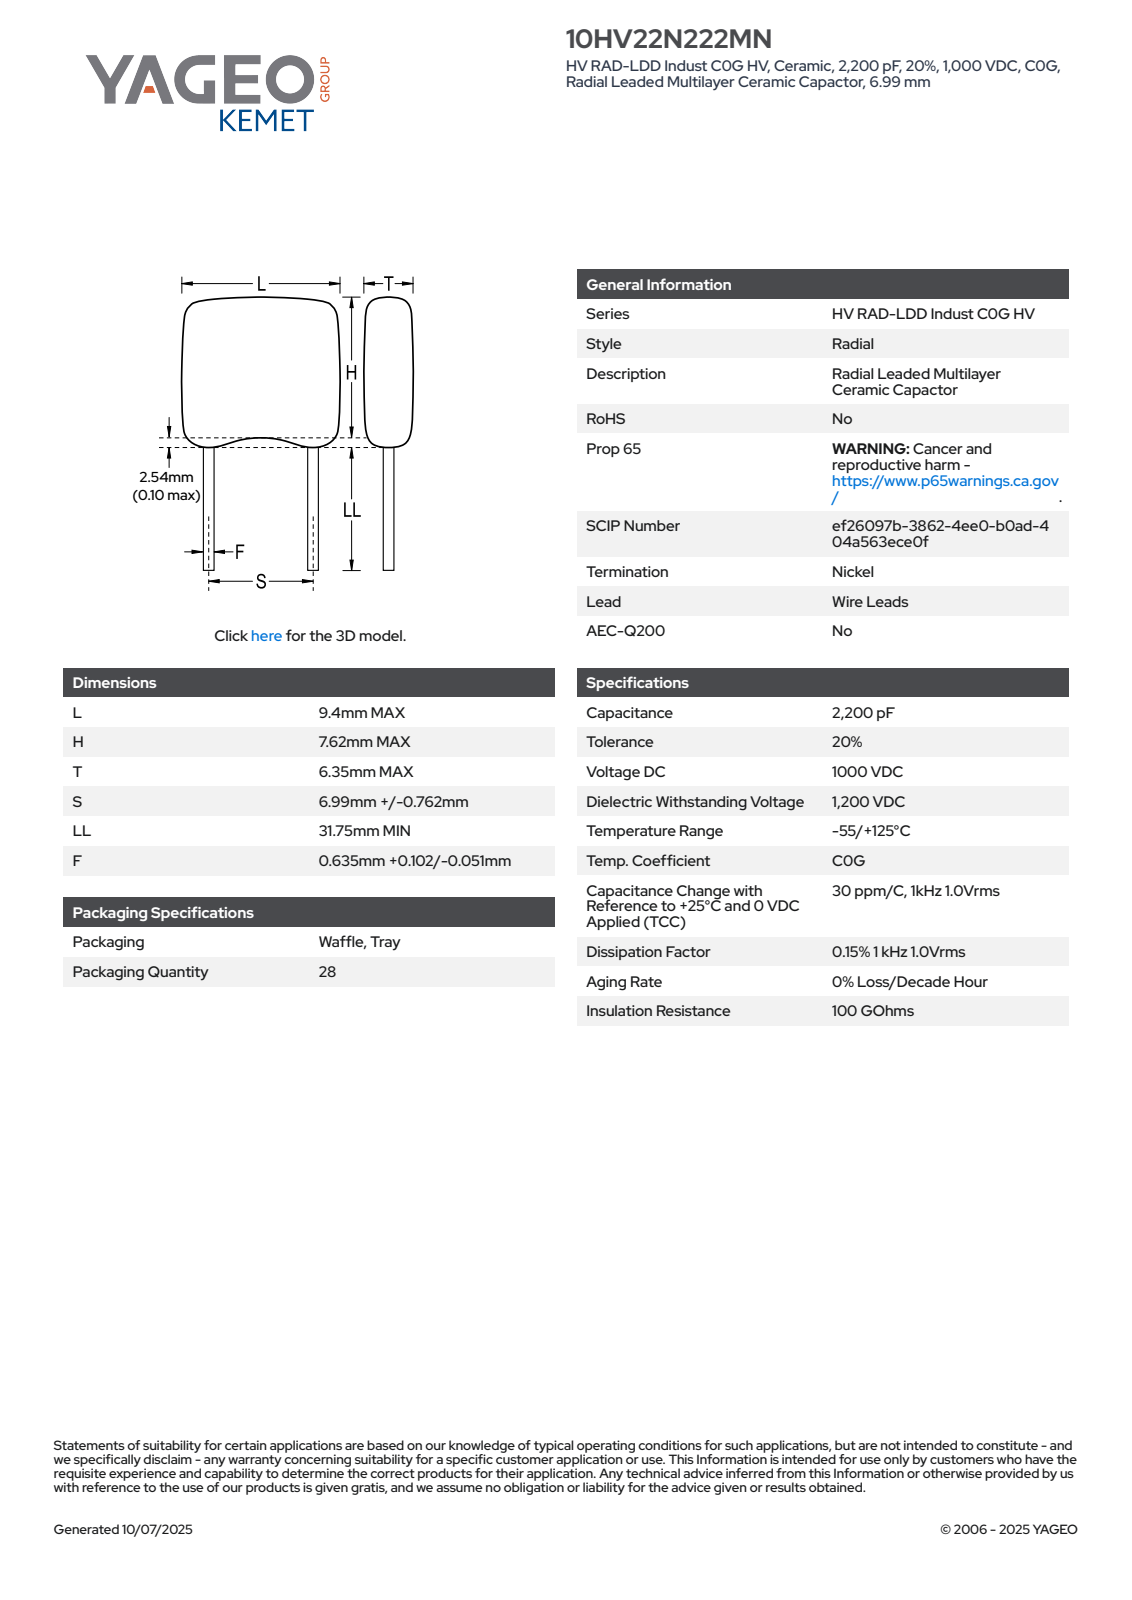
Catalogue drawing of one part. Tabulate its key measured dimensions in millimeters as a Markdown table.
| quantity | value |
| --- | --- |
| part name | CCRM_RCST_HV22_L9.4H7.62T6.35S6.99LL31.75F0.737 |
| STEP written by | SolidWorks 2021 (AUTOMOTIVE_DESIGN) |
| units | millimeters |
| bodies | 4 solids, 98 faces (66 planar, 20 cylindrical, 12 other) |
| overall size | 12.38 × 9.4 × 6.36 |
| volume | 483 mm³ |
| surface area | 389 mm² |
| round bosses / shafts (diameter × count) | 0.74 × 2 |
| partial cylindrical surfaces (radius × count) | 1 × 8, 0.5 × 4 |
| main face-to-face distances | 6.35, 9.4, 9.2, 3.17, 12.37, 8.44, 5.27, 3.93, 7.25, 4.08 |
